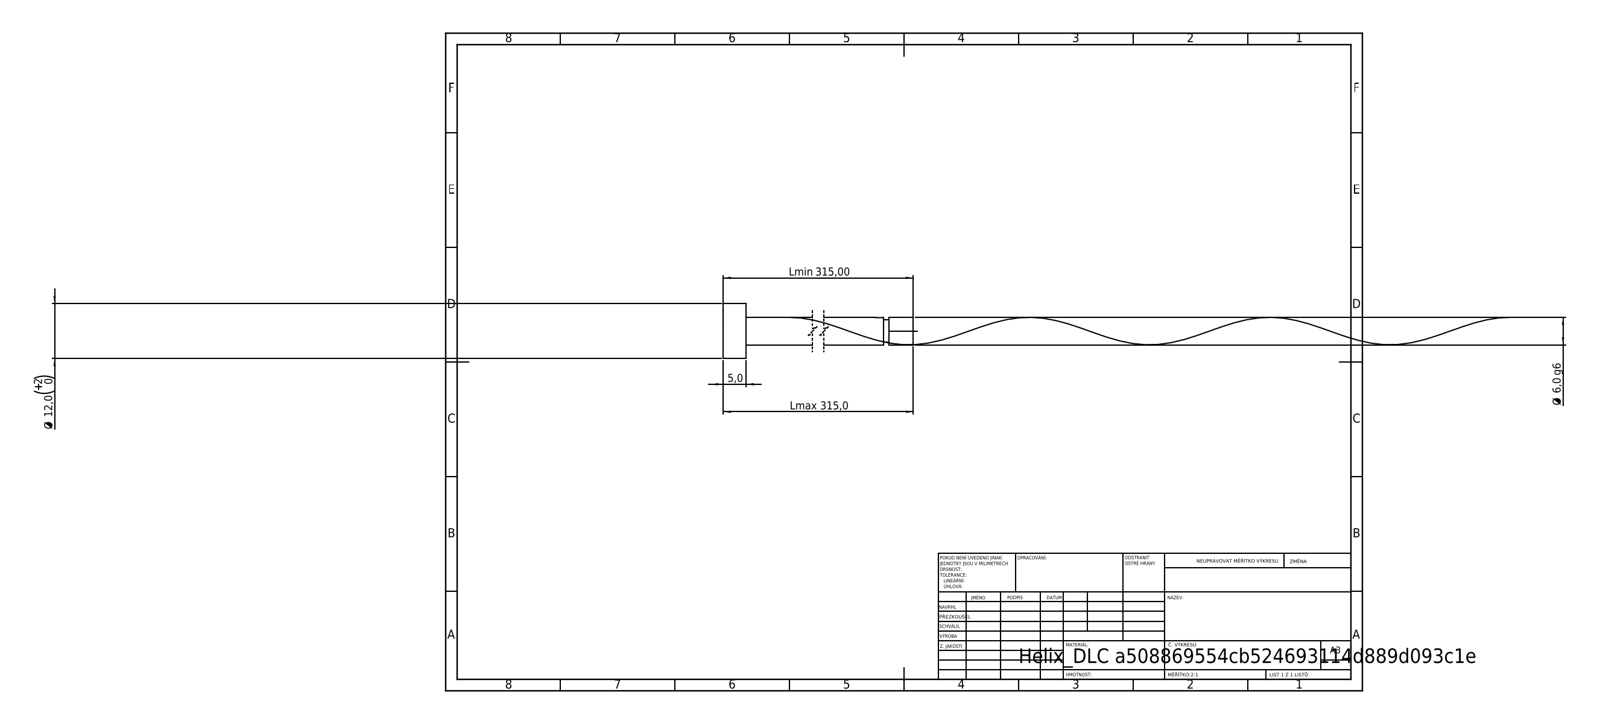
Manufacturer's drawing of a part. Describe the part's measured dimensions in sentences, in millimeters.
Its 3-D file was written by "SolidWorks 2019 (CONFIG_CONTROL_DESIGN)". It is 1 solid with 21 faces: 6 planar, 14 cylindrical and 1 other. Overall it measures 315 by 12 by 12 millimeters. Its volume is 9 233 cubic millimeters and its surface area 6 371 square millimeters. Round bosses or shafts: 1 of diameter 12, 1 of diameter 6, 1 of diameter 4.8. The main face-to-face distances are 5, 315, 310, 309.69, 304.69, 5.31, 308.49, 303.49, 1.2, 6.51.
